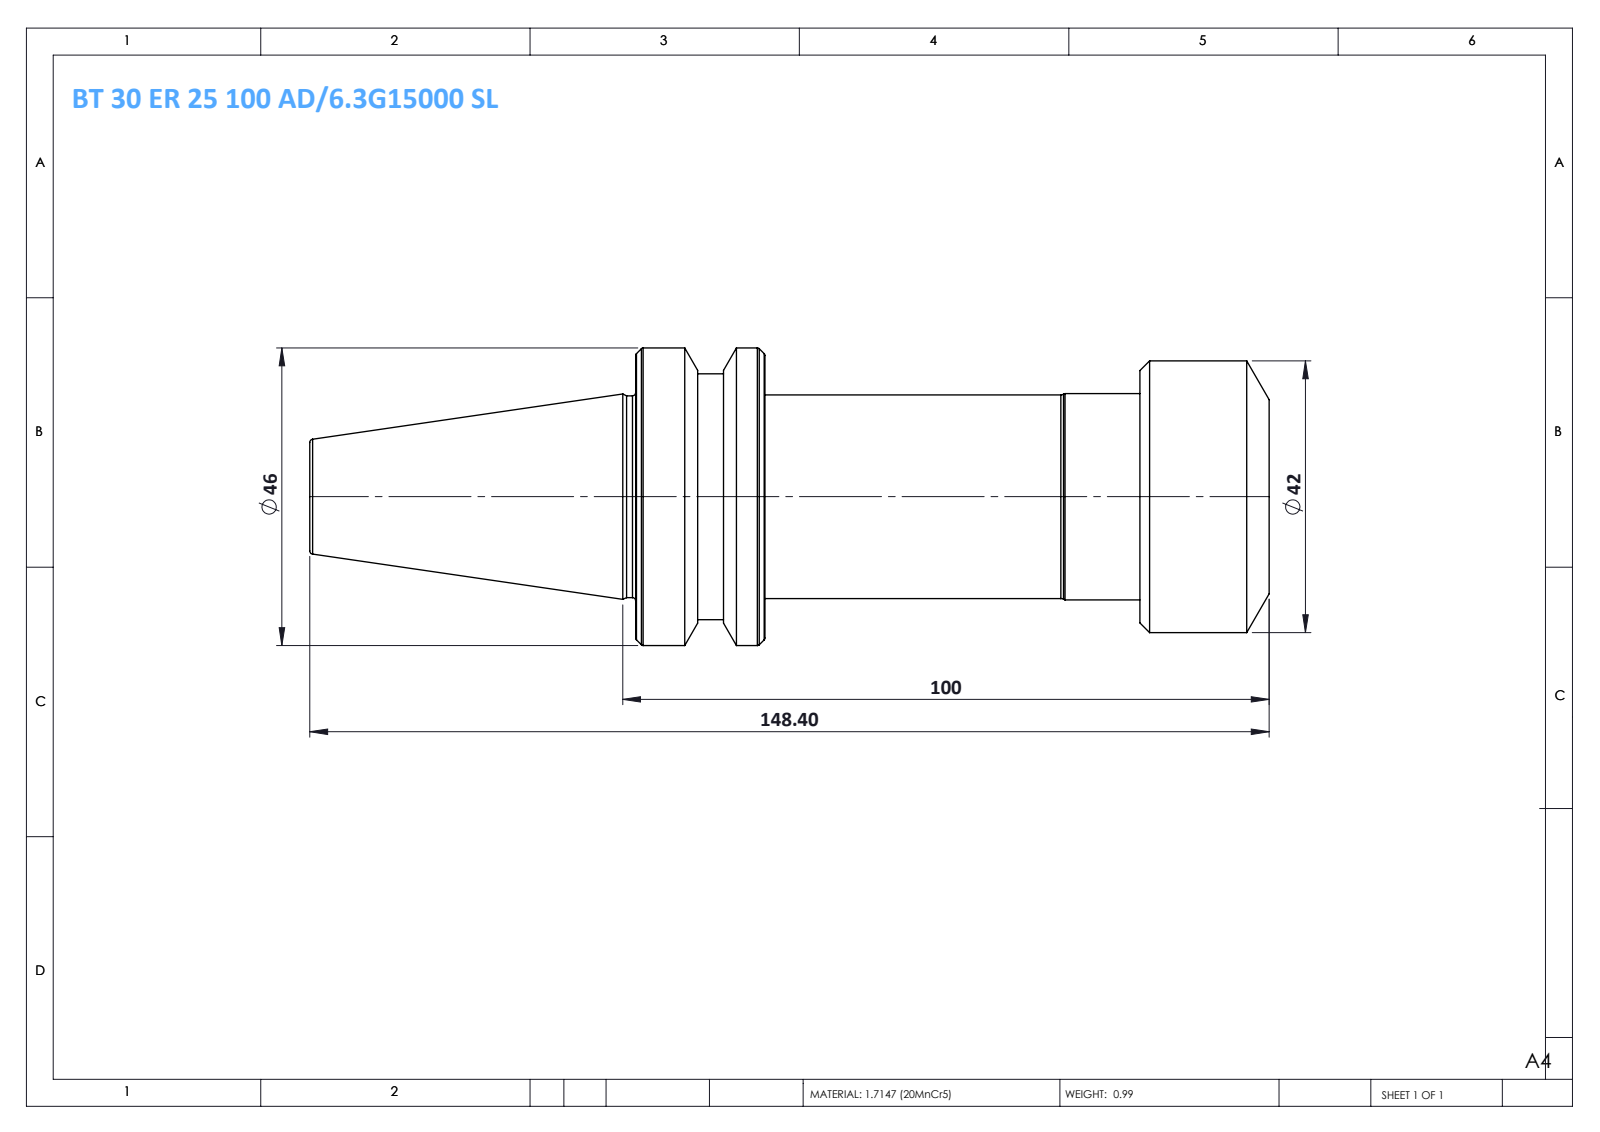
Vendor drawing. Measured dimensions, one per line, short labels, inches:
name: BT 30 ER 20 100 AD-6.3G15000 SL
written by: SolidWorks 2014 (CONFIG_CONTROL_DESIGN)
unit: in
bodies: 1 solid, 53 faces (7 planar, 14 cylindrical, 32 other)
size: 5.843 × 1.811 × 1.811
volume: 7.758 in³; area: 29.63 in²
bosses: 1× ⌀1.811, 1× ⌀1.654, 1× ⌀1.496, 1× ⌀1.256, 1× ⌀1.24, 1× ⌀1.228
face distances: 3.071, 0.787, 3.858, 2.283, 5.843, 5.055, 2.772, 1.984, 3.323, 2.535
